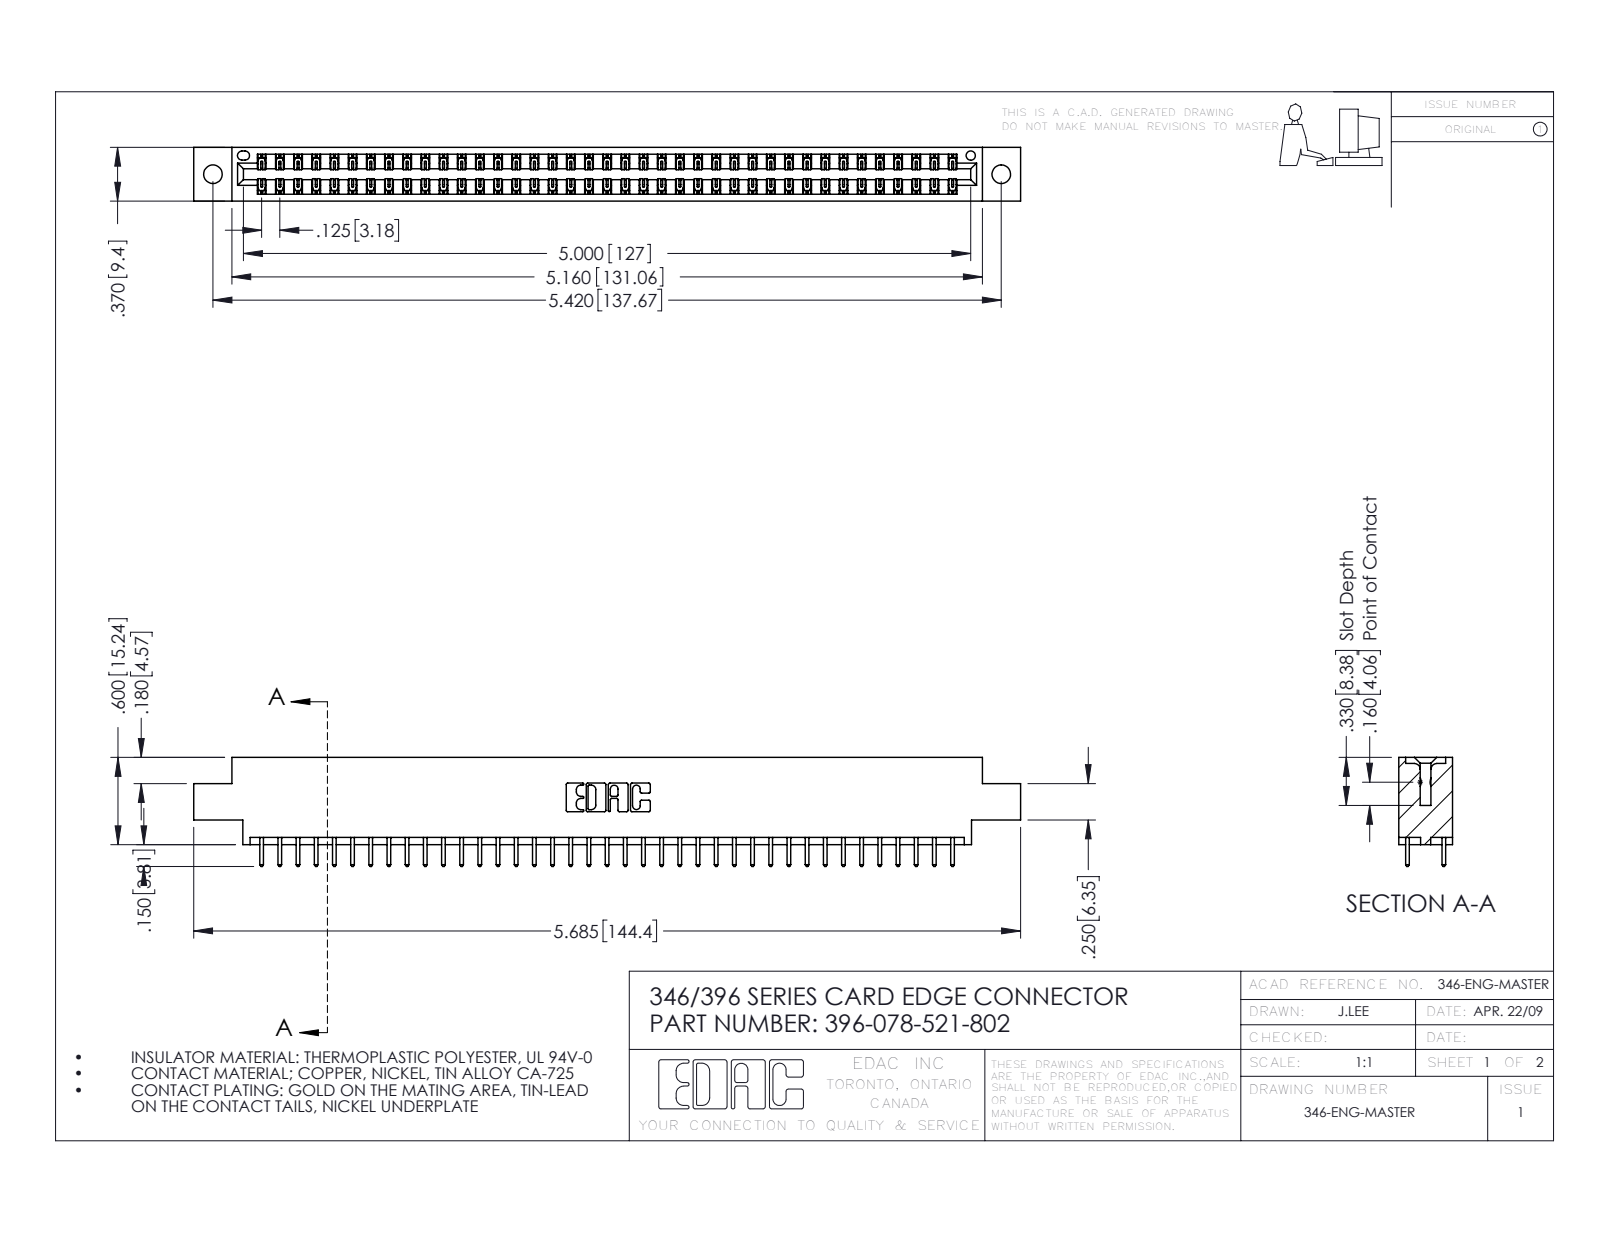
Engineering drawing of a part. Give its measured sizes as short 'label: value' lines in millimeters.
name: 396-078-521-802; 346 Part_0.170 Offset - 0.128 Dia; 345-292-001_345-293-121
written by: SolidWorks 2016 (CONFIG_CONTROL_DESIGN)
unit: mm
bodies: 79 solids, 4182 faces (2810 planar, 1372 cylindrical, 0 other)
size: 144.4 × 19.1 × 9.4
volume: 13 800 mm³; area: 18 660 mm²
holes: 2× ⌀3.3, 1× ⌀1.6
rounds: 117× R0.2, 78× R0.3, 22× R0.3, 6× R0.2, 6× R0.8, 3× R0.7, 2× R0.4, 2× R0.6
face distances: 1.2, 8.2, 9.4, 6.4, 1.8, 7.6, 0.6, 7, 3.8, 5.6
hole spacings: 6.2, 132.4, 137.7
